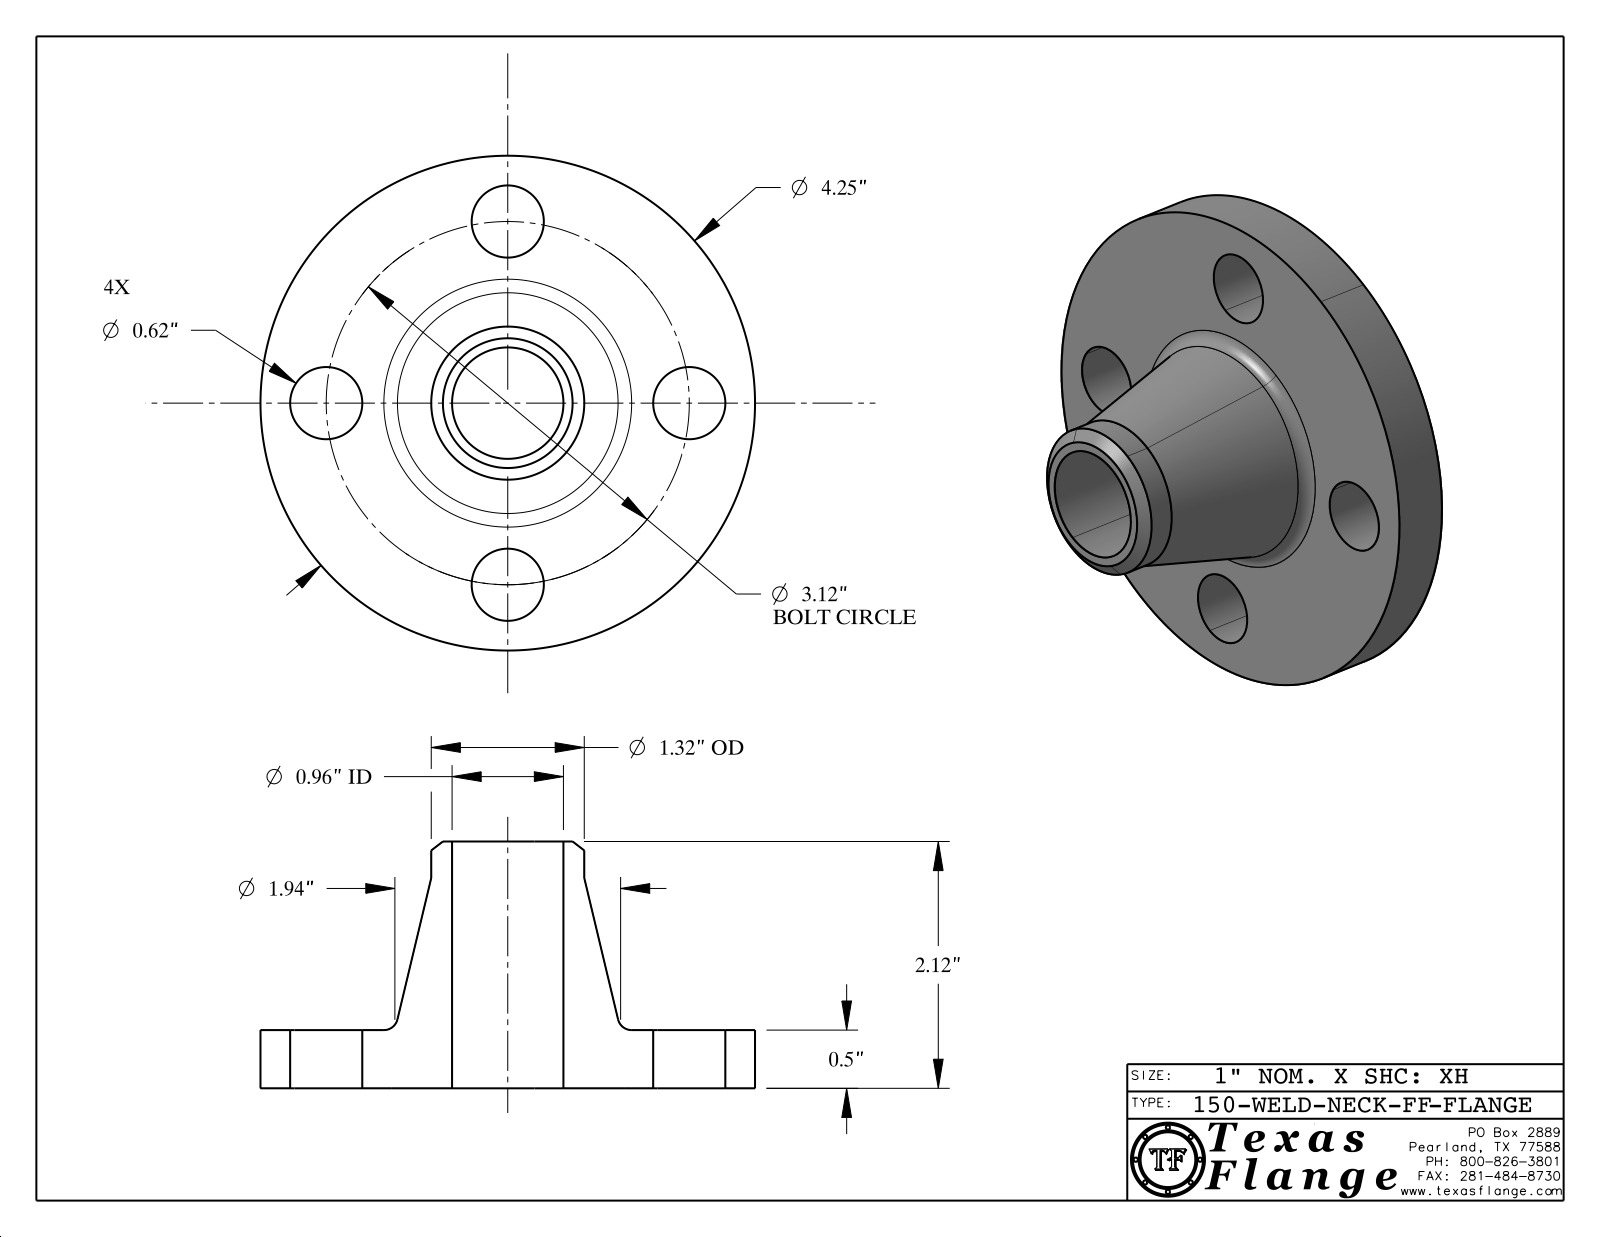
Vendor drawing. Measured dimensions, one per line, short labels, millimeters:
name: 150-WELD-NECK-FF
written by: CATIA V5 STEP AP214 (AUTOMOTIVE_DESIGN)
unit: mm
bodies: 1 solid, 409 faces (369 planar, 34 cylindrical, 6 other)
size: 108 × 108 × 53.8
volume: 133 300 mm³; area: 30 790 mm²
holes: 4× ⌀15.7, 1× ⌀12.6, 1× ⌀24.3
bosses: 8× ⌀0.8, 1× ⌀108, 1× ⌀33.4, 1× ⌀9.9
face distances: 12.7, 53.8, 41.1, 12.3, 0.4, 41.5, 3.8, 3.7, 0.7, 2.4
hole spacings: 39.6, 56, 30.3, 73.2, 79.2, 39.6
